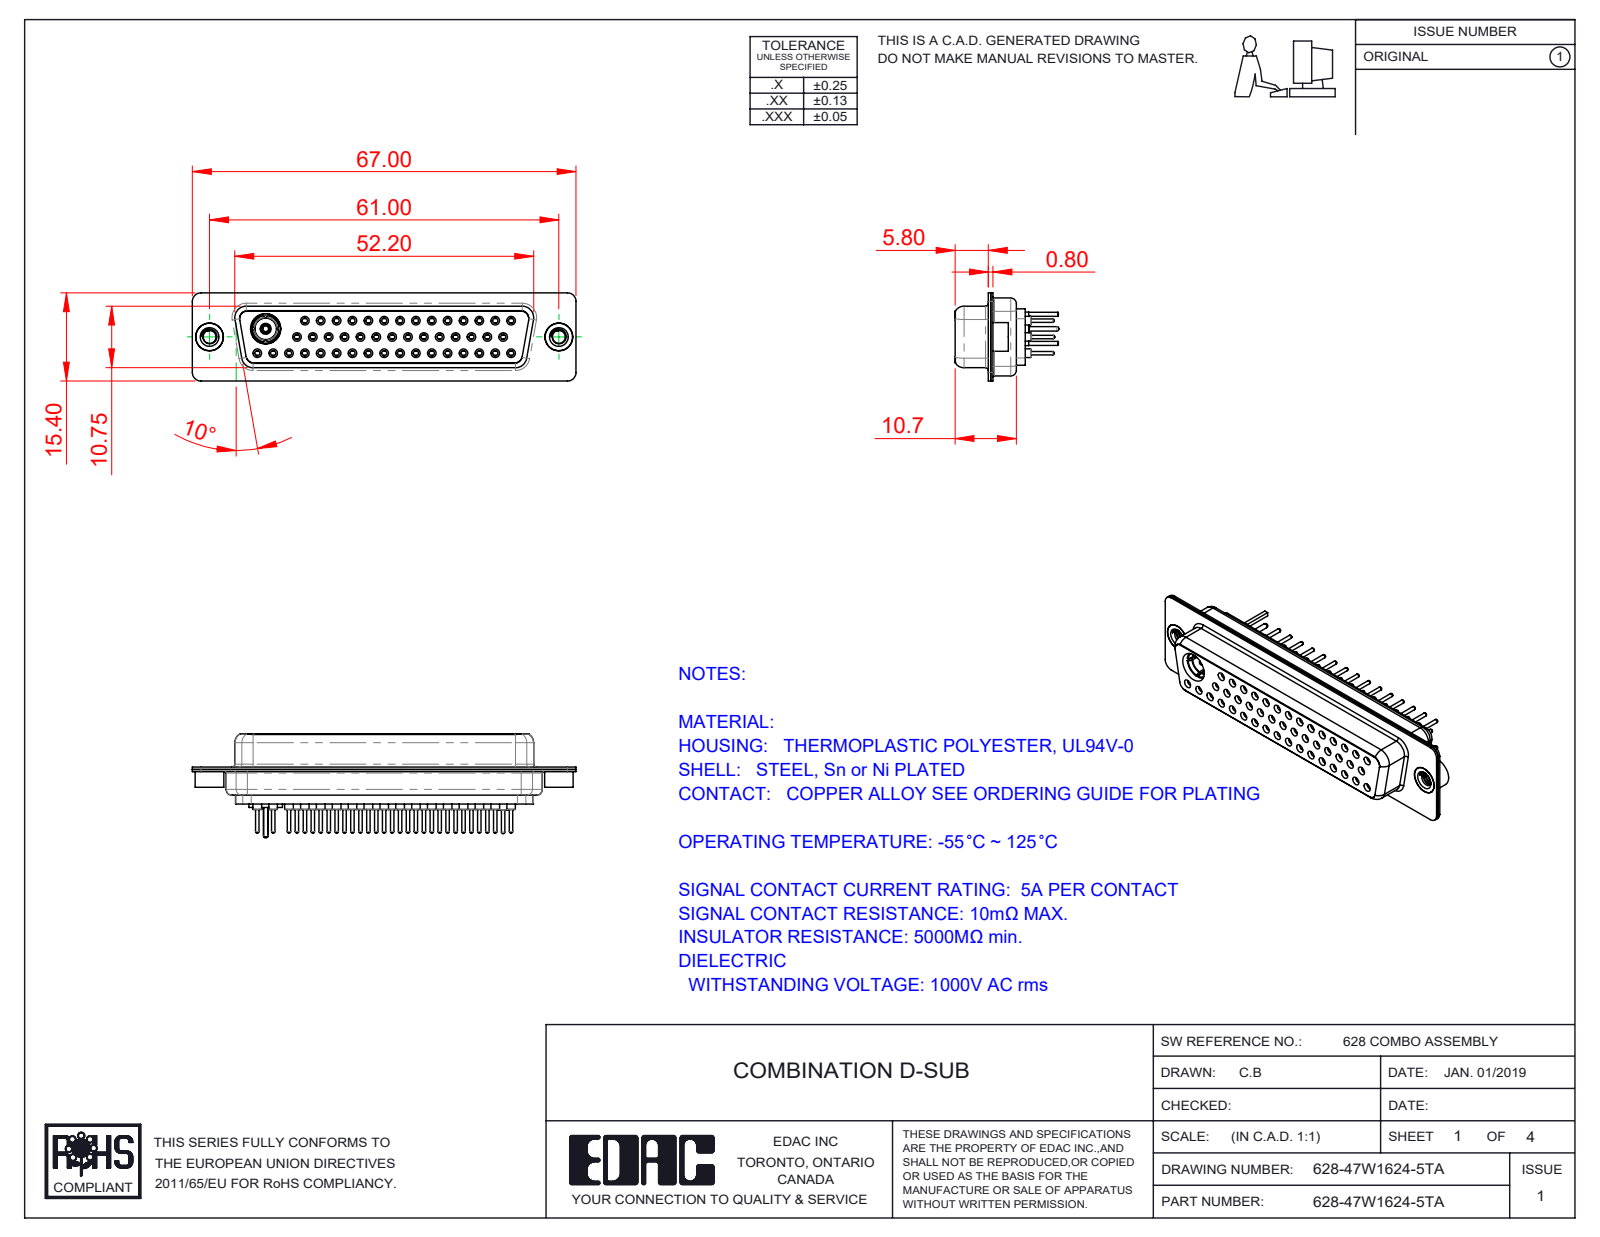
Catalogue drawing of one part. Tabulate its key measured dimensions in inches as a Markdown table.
| quantity | value |
| --- | --- |
| part name | 628Combo Shell Rear_50 Contacts; 628Combo Housing_47W1; 628Combo Contact Row 3_24; Co-Ax Plug Assy_St (+8 more) |
| STEP written by | SolidWorks 2016 (CONFIG_CONTROL_DESIGN) |
| units | inches |
| bodies | 55 solids, 2921 faces (811 planar, 1050 cylindrical, 1060 other) |
| overall size | 2.638 × 0.715 × 0.606 |
| volume | 0.43 in³ |
| surface area | 23.06 in² |
| round holes (diameter × count) | 0.043 × 47, 0.059 × 46, 0.035 × 45, 0.079 × 45, 0.063 × 31, 0.067 × 14, 0.191 × 3, 0.089 × 2, 0.157 × 2, 0.159 × 2, 0.111 × 1, 0.13 × 1 |
| round bosses / shafts (diameter × count) | 0.087 × 46, 0.024 × 46, 0.063 × 15, 0.197 × 3, 0.195 × 2, 0.189 × 2, 0.23 × 1, 0.205 × 1 |
| partial cylindrical surfaces (radius × count) | 0.059 × 16, 0.053 × 12, 0.079 × 12, 0.063 × 8, 0.01 × 4, 0.02 × 4, 0.024 × 4, 0.026 × 4 |
| main face-to-face distances | 0.016, 0.238, 0.254, 0.446, 0.074, 0.482, 0.244, 0.228, 0.407, 0.43 |
| hole center spacings | 0.124, 0.109, 0.218, 0.327, 0.436, 0.545, 0.654, 0.763 |
